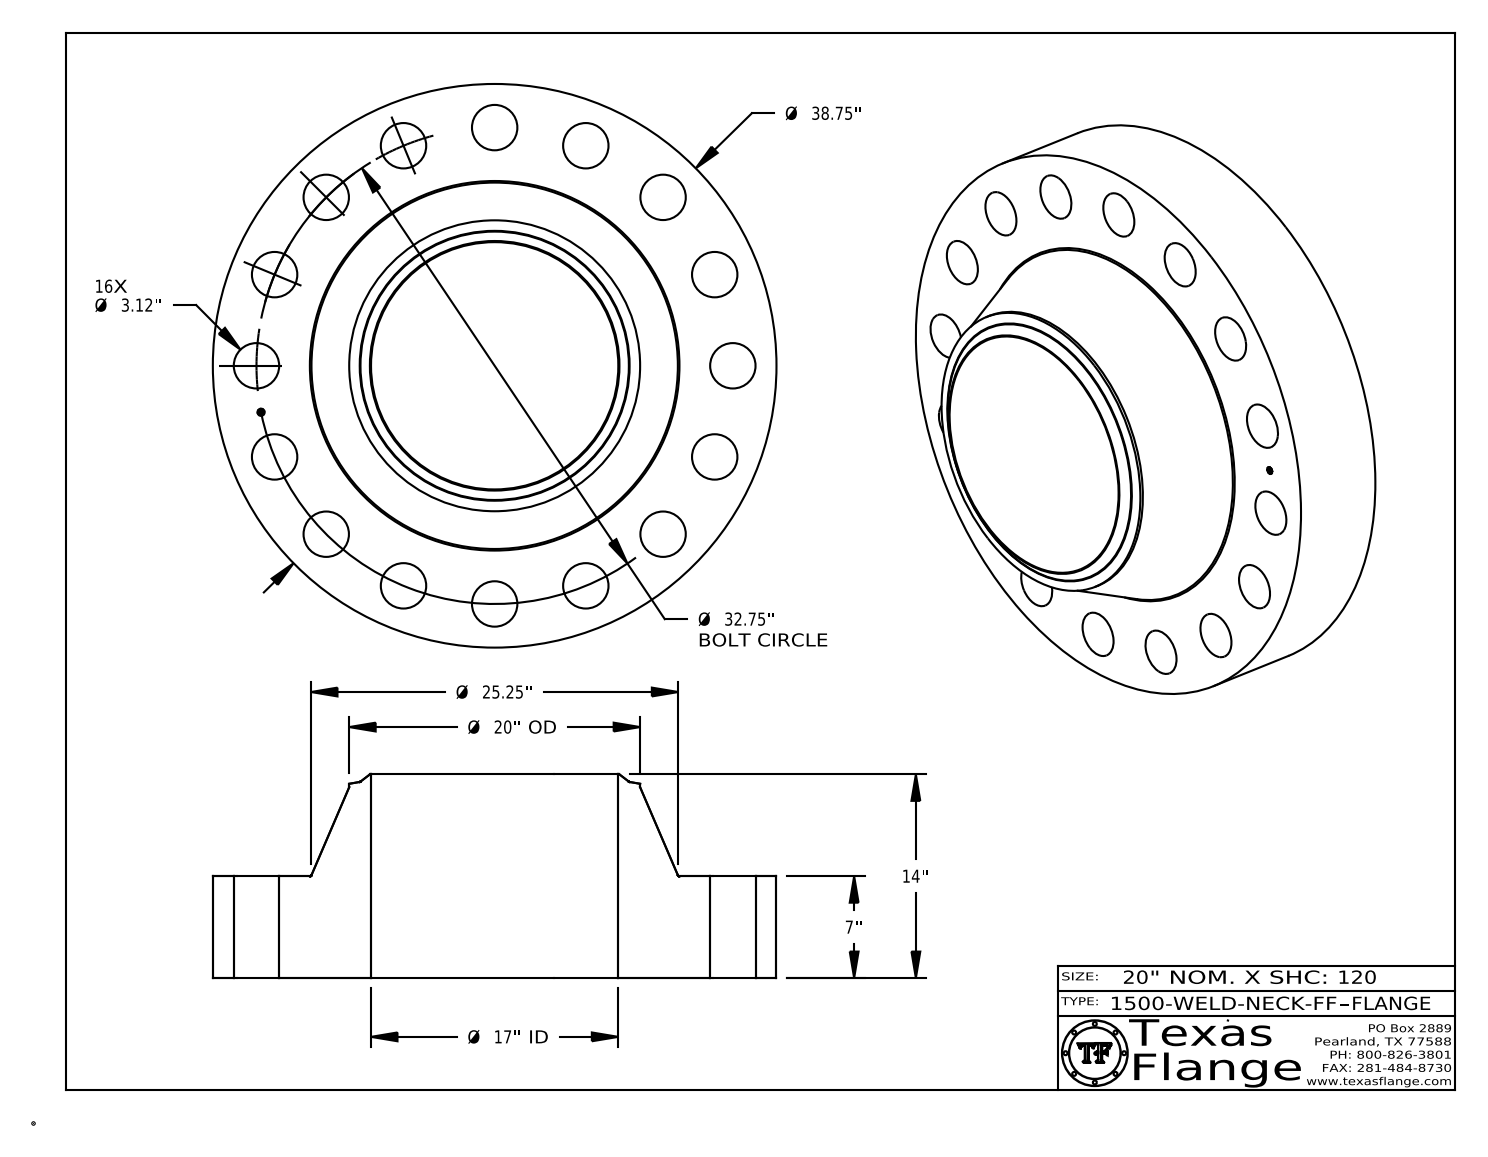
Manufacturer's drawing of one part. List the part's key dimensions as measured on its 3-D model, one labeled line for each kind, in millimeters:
Part name (STEP PRODUCT): 1500-WELD-NECK-FF
STEP written by: CATIA V5 STEP AP214 (AUTOMOTIVE_DESIGN)
Units: millimetres
Bodies: 1 solid, 436 faces (368 planar, 58 cylindrical, 10 other)
Overall size (bounding box): 984.3 × 984.3 × 355.6
Volume: 113 600 000 mm³ · Surface area: 3 012 000 mm²
Round holes (diameter × count): ⌀79.2 ×16, ⌀12.6 ×1, ⌀431.8 ×1
Round bosses / shafts (diameter × count): ⌀0.8 ×8, ⌀984.3 ×1, ⌀508 ×1, ⌀9.9 ×1
Main face-to-face distances: 177.8, 355.6, 177.4, 0.4, 178.2, 3.8, 3.7, 0.7, 2.4, 3.1
Hole centre spacings: 462.2, 415.9, 318.3, 588.2, 768.5, 162.3, 162.3, 691.6
